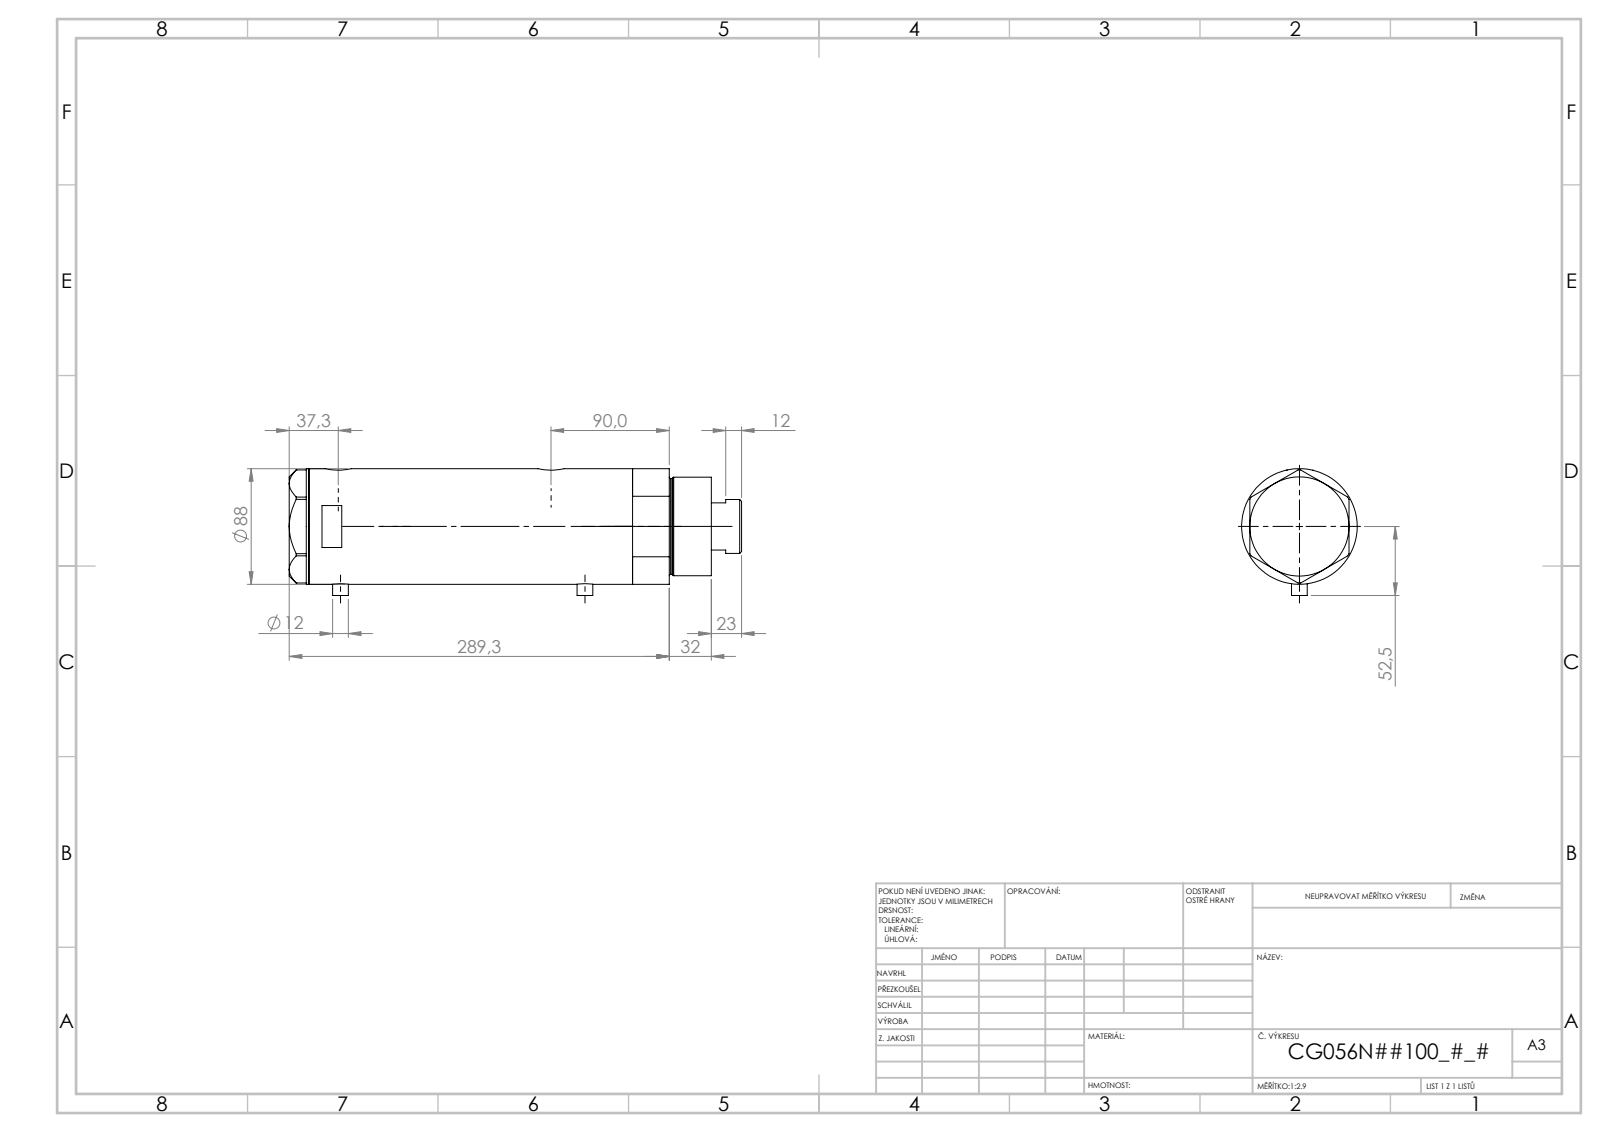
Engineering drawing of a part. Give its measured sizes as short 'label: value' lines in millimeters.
name: V270CG_FRONT; V270CG_VC; V270CG_BACK; V270CG_MIDDLE
written by: SolidWorks 2019 (CONFIG_CONTROL_DESIGN)
unit: mm
bodies: 4 solids, 126 faces (53 planar, 53 cylindrical, 20 other)
size: 324.47 × 89.1 × 88
volume: 1 662 000 mm³; area: 238 693 mm²
holes: 2× ⌀5, 2× ⌀12.5, 2× ⌀13.16, 2× ⌀20, 1× ⌀14.5, 1× ⌀42, 1× ⌀43.5, 1× ⌀56, 1× ⌀60, 1× ⌀80
bosses: 2× ⌀12, 1× ⌀88, 1× ⌀75, 1× ⌀73, 1× ⌀41
face distances: 174.4, 26, 148.4, 15, 41, 189.4, 286.47, 301.47, 260.47, 112.07
hole spacings: 1.7, 25.8, 150.3, 152, 176.1, 177.8
